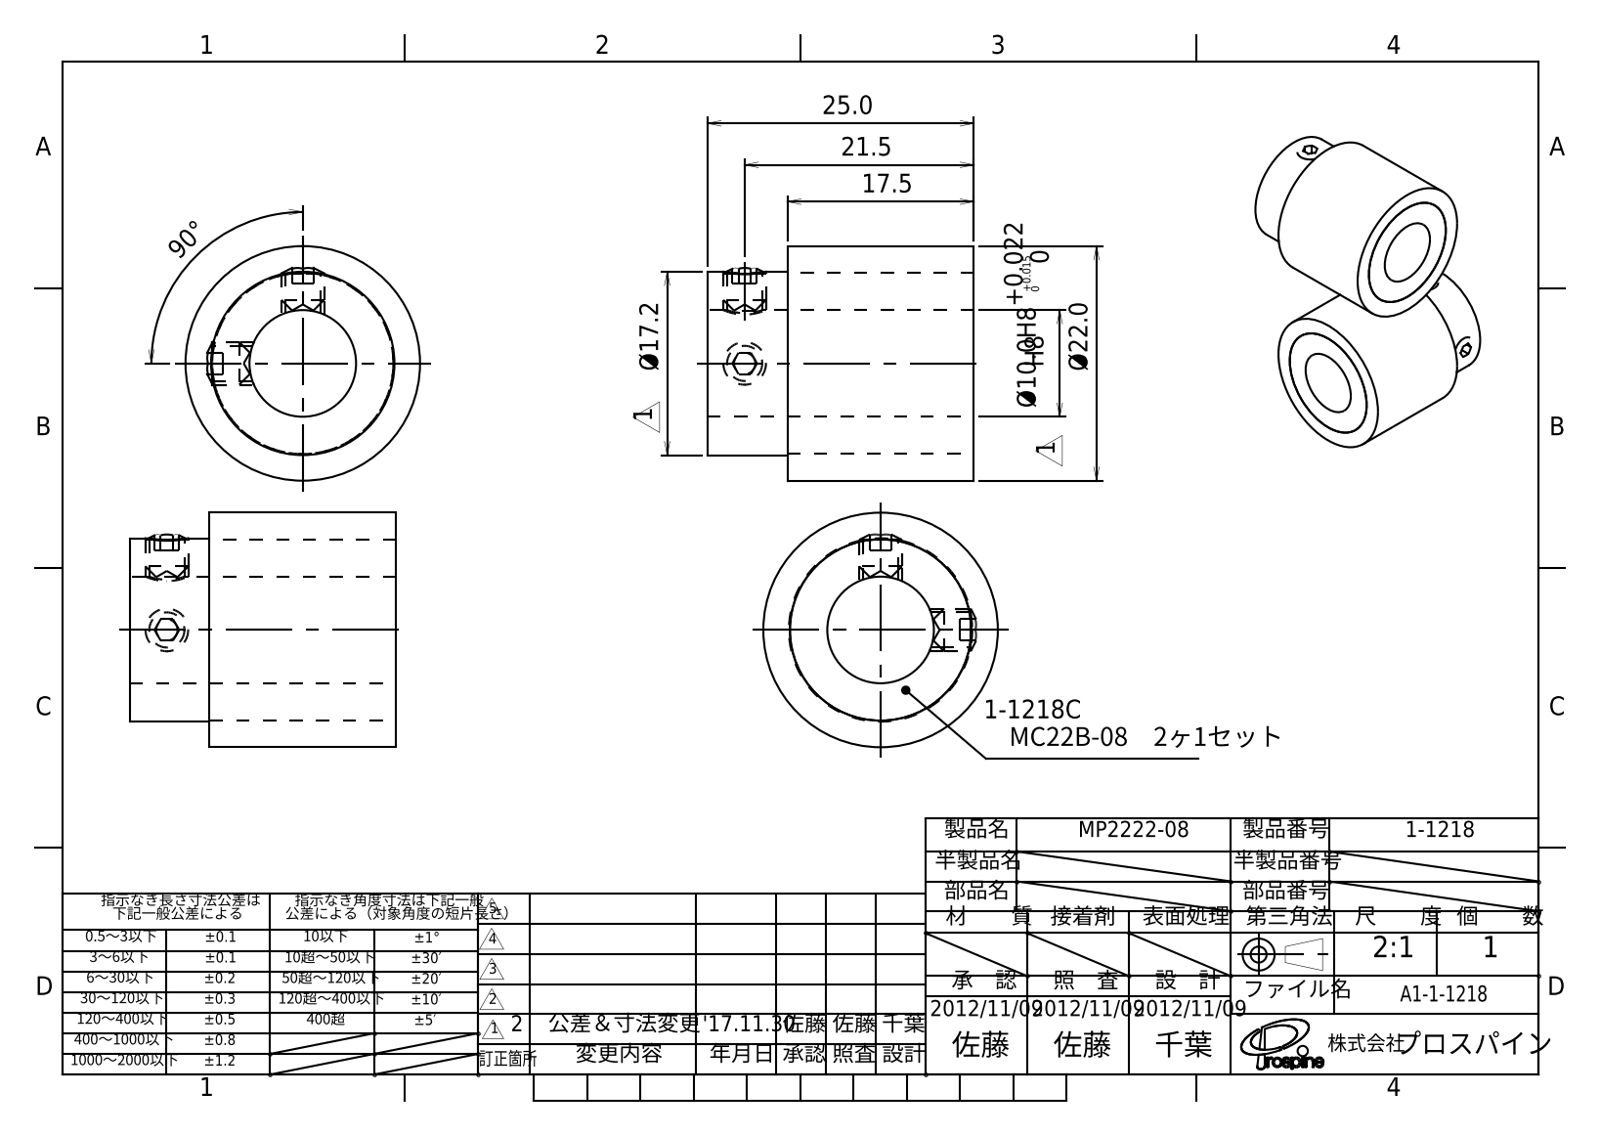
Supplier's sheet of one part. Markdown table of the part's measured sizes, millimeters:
| quantity | value |
| --- | --- |
| STEP written by | PSStep 10.0 (CONFIG_CONTROL_DESIGN) |
| units | millimeters |
| bodies | 6 solids, 56 faces (33 planar, 11 cylindrical, 12 other) |
| overall size | 25 × 22 × 22 |
| volume | 6 516 mm³ |
| surface area | 5 214 mm² |
| round holes (diameter × count) | 3.3 × 2, 10 × 1, 17 × 1 |
| round bosses / shafts (diameter × count) | 4 × 2, 22 × 1, 17.2 × 1 |
| main face-to-face distances | 17.5, 7.5, 25, 2, 8.45, 6.46, 6.45, 8.46 |
